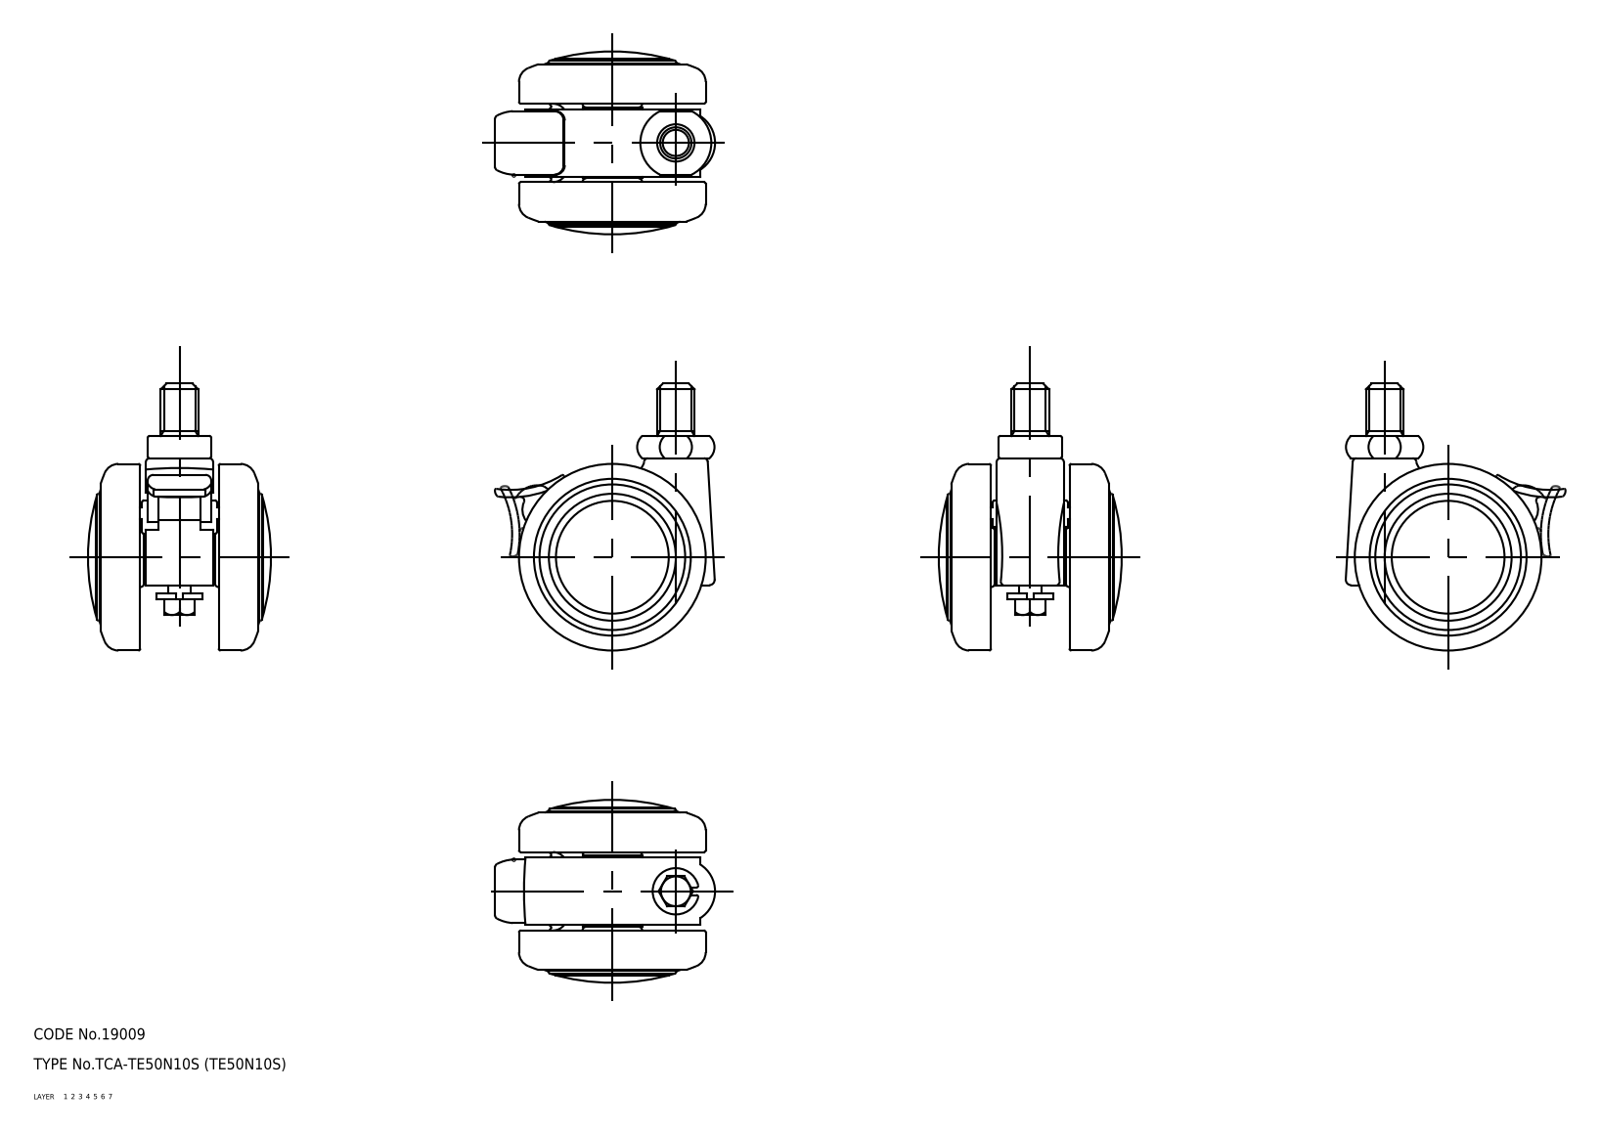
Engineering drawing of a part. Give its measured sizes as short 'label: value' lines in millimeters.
name: wheel; main shaft; lever; TE50N10S_3164_36
written by: CADfix (AUTOMOTIVE_DESIGN)
unit: mm
bodies: 5 solids, 231 faces (0 planar, 0 cylindrical, 231 other)
size: 71.5 × 59.42 × 49
volume: 63 271 mm³; area: 27 532 mm²
